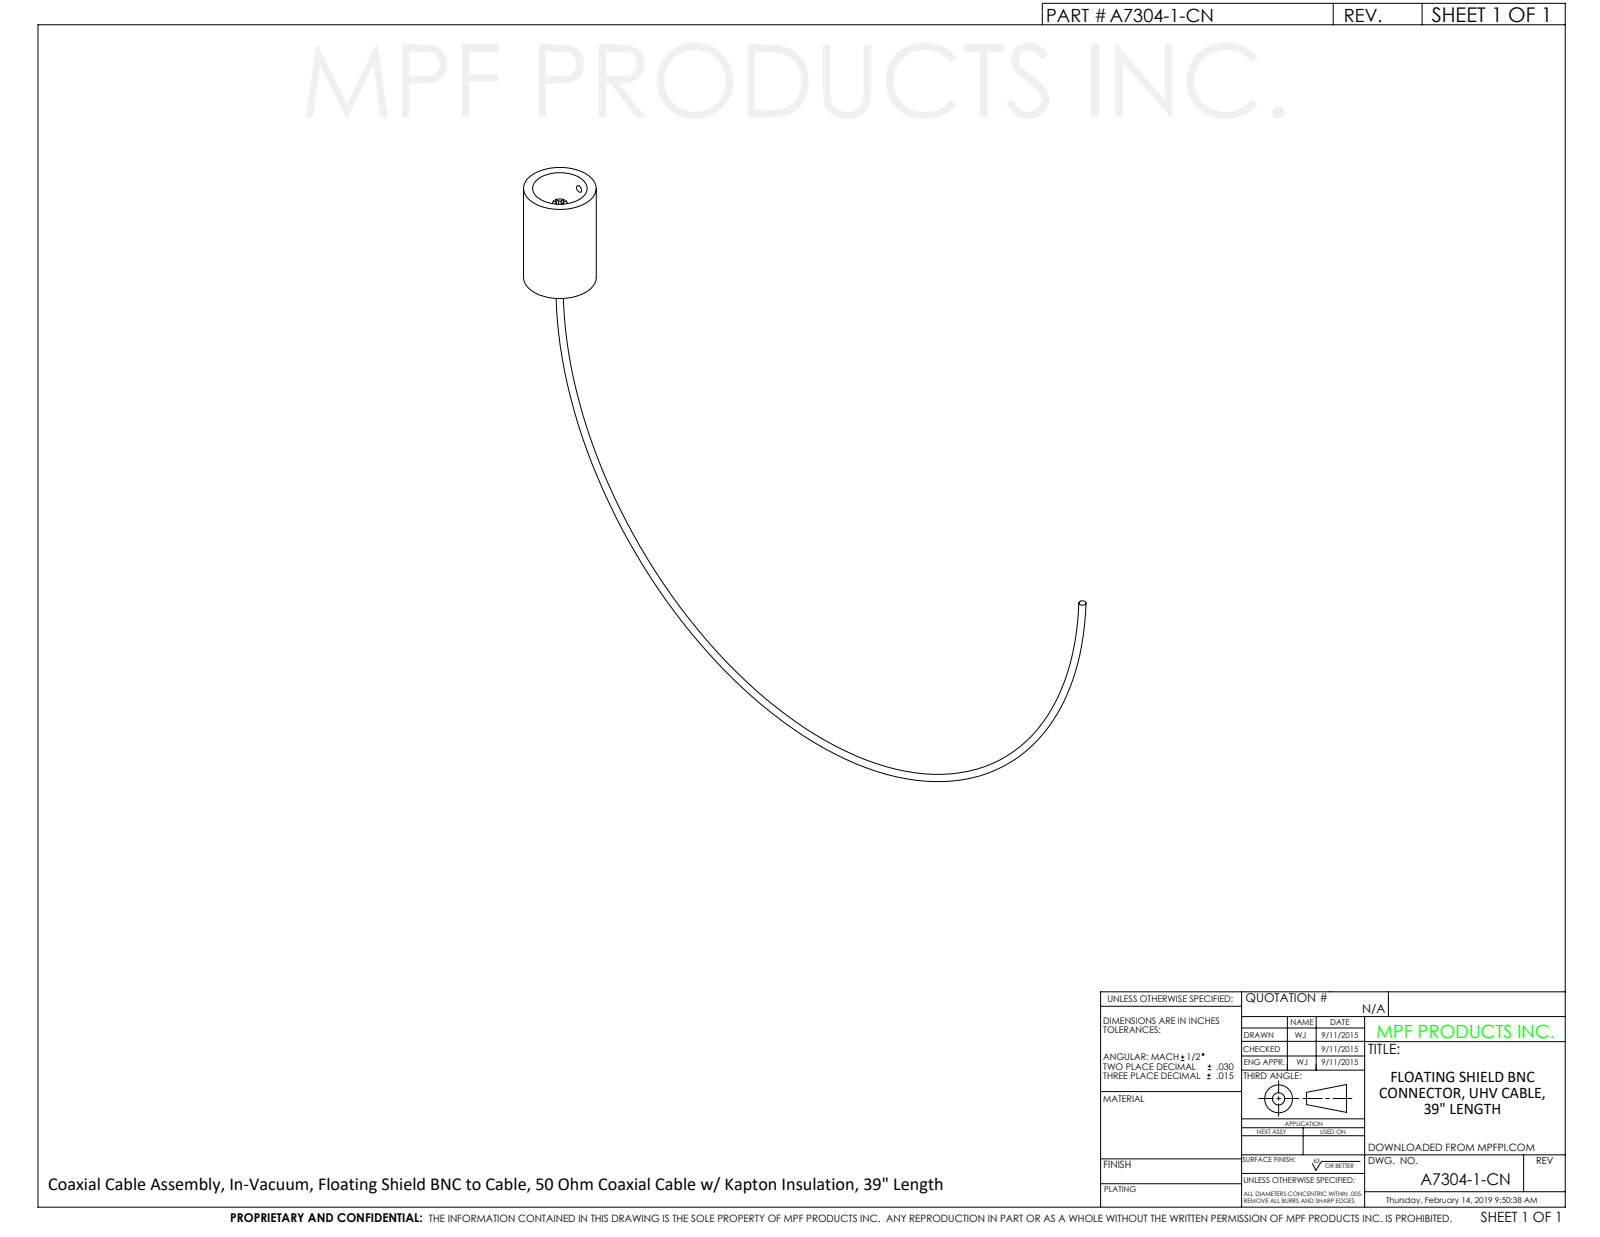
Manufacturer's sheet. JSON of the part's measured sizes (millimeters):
{"part_name": "A7304-1-CN", "step_written_by": "SolidWorks 2012 (CONFIG_CONTROL_DESIGN)", "units": "millimeters", "bodies": {"solids": 1, "faces": 47, "planar": 22, "cylindrical": 20, "other": 5}, "overall_size": [272.1, 173.6, 25.4], "volume_mm3": 16300, "surface_area_mm2": 8845, "round_holes": [[2.5, 3], [5.1, 1], [19.1, 1]], "round_bosses_or_shafts": [[25.4, 1], [5.1, 1]], "face_to_face_distances": [38.1, 1, 0.5, 31.8, 6.3, 10.7, 9.7, 25.5, 6.4, 12.6], "hole_center_spacings": [8.9]}
